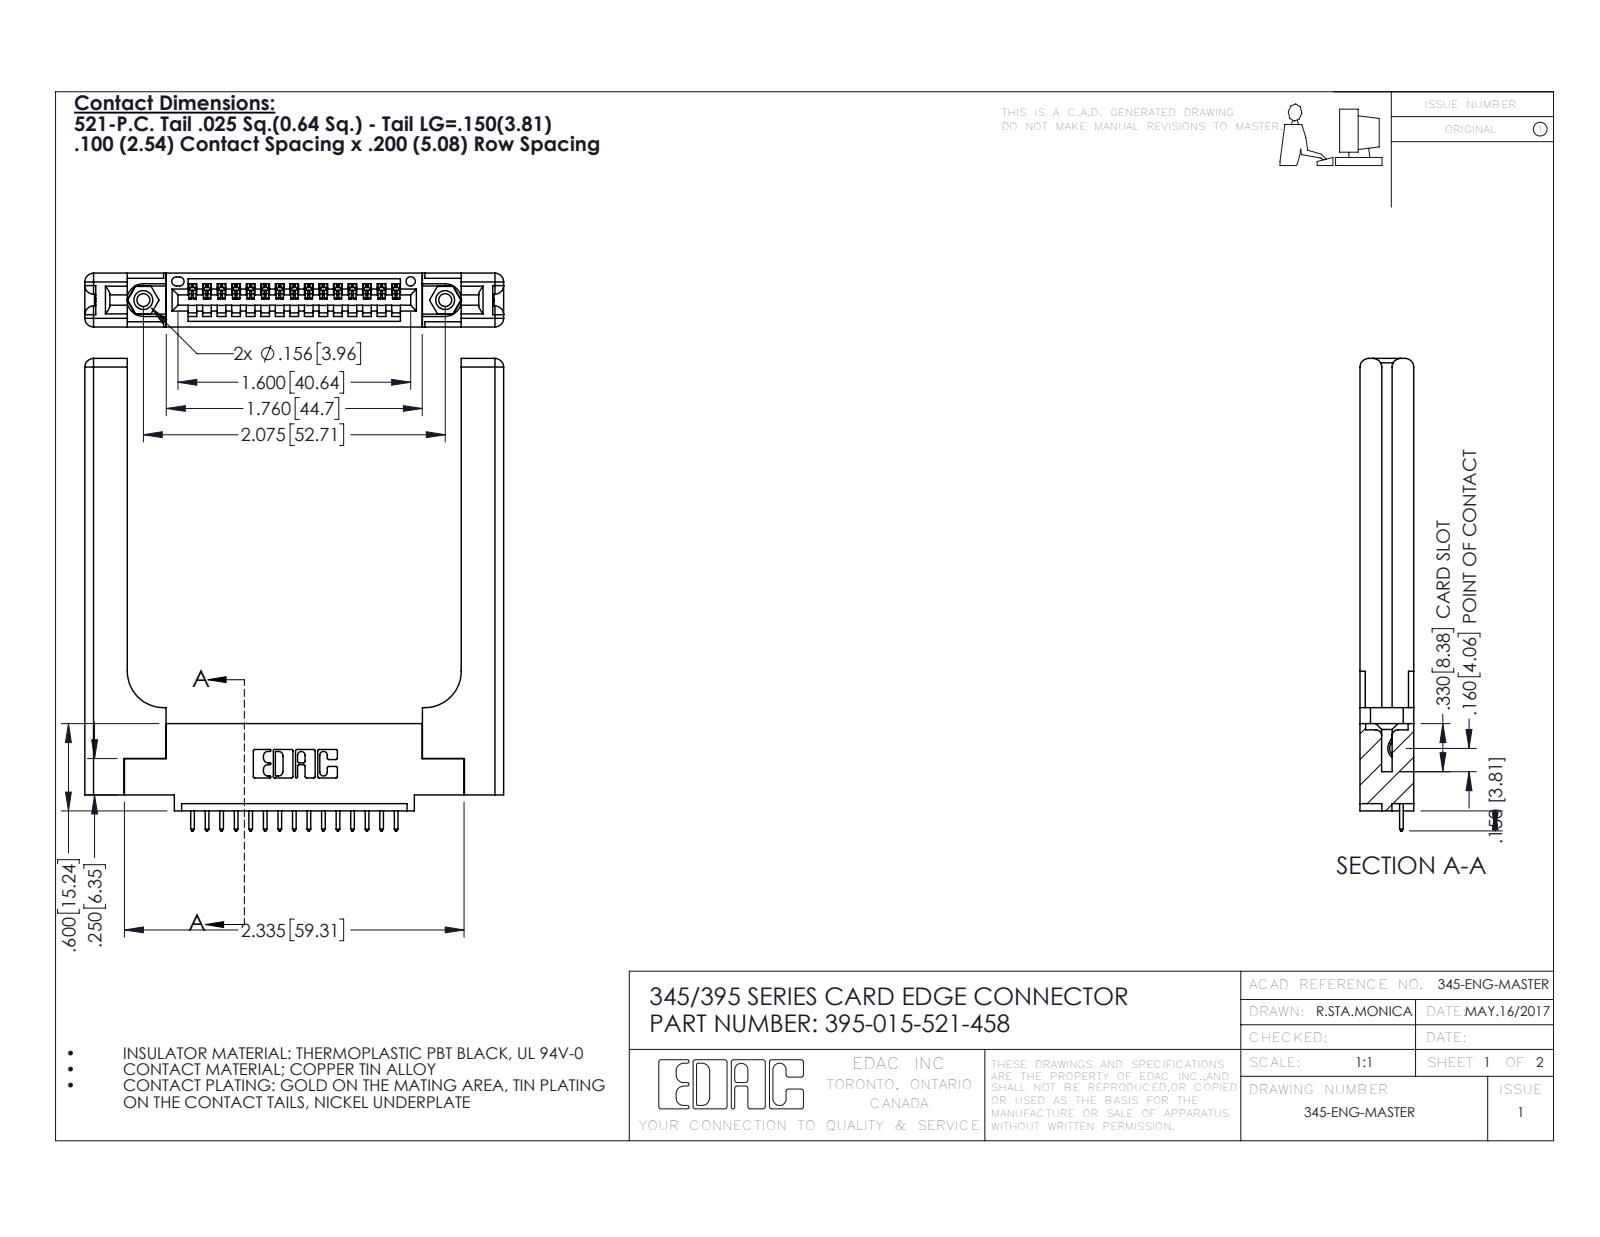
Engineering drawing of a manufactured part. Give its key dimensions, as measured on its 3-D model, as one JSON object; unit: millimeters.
{"part_name": "345-250-001_345-250-001-102; 345 Part_0.110 Offset - 0.156 Dia-TH; 345-220-058_345-220-058; 345-292-001_345-293-121 (+1 more)", "step_written_by": "SolidWorks 2016 (CONFIG_CONTROL_DESIGN)", "units": "millimeters", "bodies": {"solids": 20, "faces": 1256, "planar": 832, "cylindrical": 364, "other": 60}, "overall_size": [82.5, 73.1, 9.4], "volume_mm3": 15100, "surface_area_mm2": 13640, "round_holes": [[2.3, 2], [3.2, 2], [4, 2], [1.6, 1]], "round_bosses_or_shafts": [[3.9, 2]], "partial_cylinders_radius": [[0.2, 30], [0.3, 30], [0.3, 22], [1.5, 16], [0.2, 6], [0.8, 6], [0.7, 3], [0.8, 2]], "face_to_face_distances": [9.4, 1.8, 7.6, 3.8, 3.8, 2, 5.6, 2.5, 6.9, 0.6], "hole_center_spacings": [6.9, 46.8, 52.7]}
